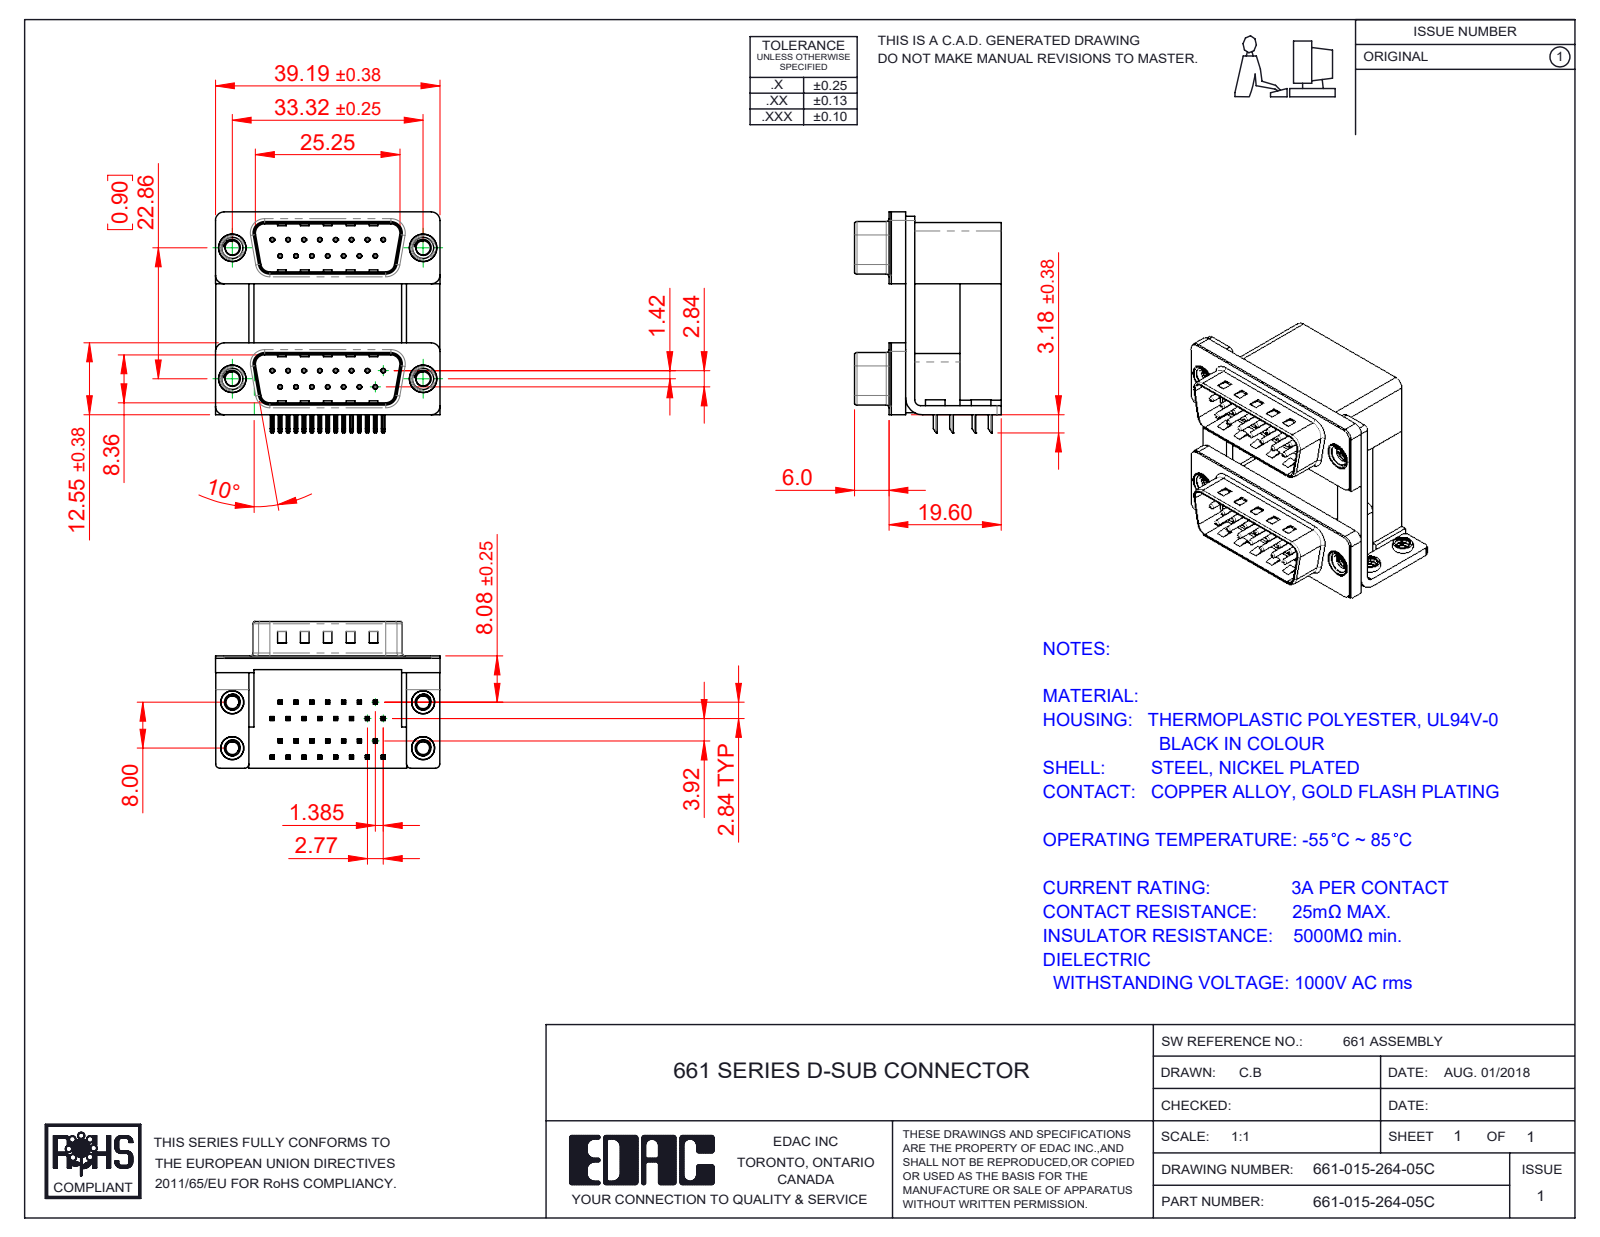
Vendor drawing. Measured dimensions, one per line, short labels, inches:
name: 661-015-264-05C; 661 Shell_15 Contacts; 661 Housing Spacer_15 Contacts H; 661 Housing Upper_15 Contacts H (+8 more)
written by: SolidWorks 2020 (CONFIG_CONTROL_DESIGN)
unit: in
bodies: 45 solids, 3106 faces (1846 planar, 938 cylindrical, 322 other)
size: 1.543 × 1.519 × 1.008
volume: 0.926 in³; area: 25.77 in²
holes: 30× ⌀0.014, 30× ⌀0.031, 4× ⌀0.089, 4× ⌀0.098, 4× ⌀0.108, 4× ⌀0.126, 4× ⌀0.138, 4× ⌀0.157, 4× ⌀0.189, 4× ⌀0.197
bosses: 30× ⌀0.03, 4× ⌀0.193, 4× ⌀0.187, 4× ⌀0.157, 4× ⌀0.154, 4× ⌀0.134
rounds: 120× R0.01, 60× R0.005, 16× R0.02, 15× R0.059, 8× R0.03, 8× R0.035, 8× R0.063, 8× R0.079
face distances: 0.016, 0.9, 0.472, 0.756, 0.283, 0.657, 0.374, 0.098, 0.488, 0.421
hole spacings: 0.124, 0.109, 0.907, 0.218, 0.926, 0.327, 0.9, 0.957
